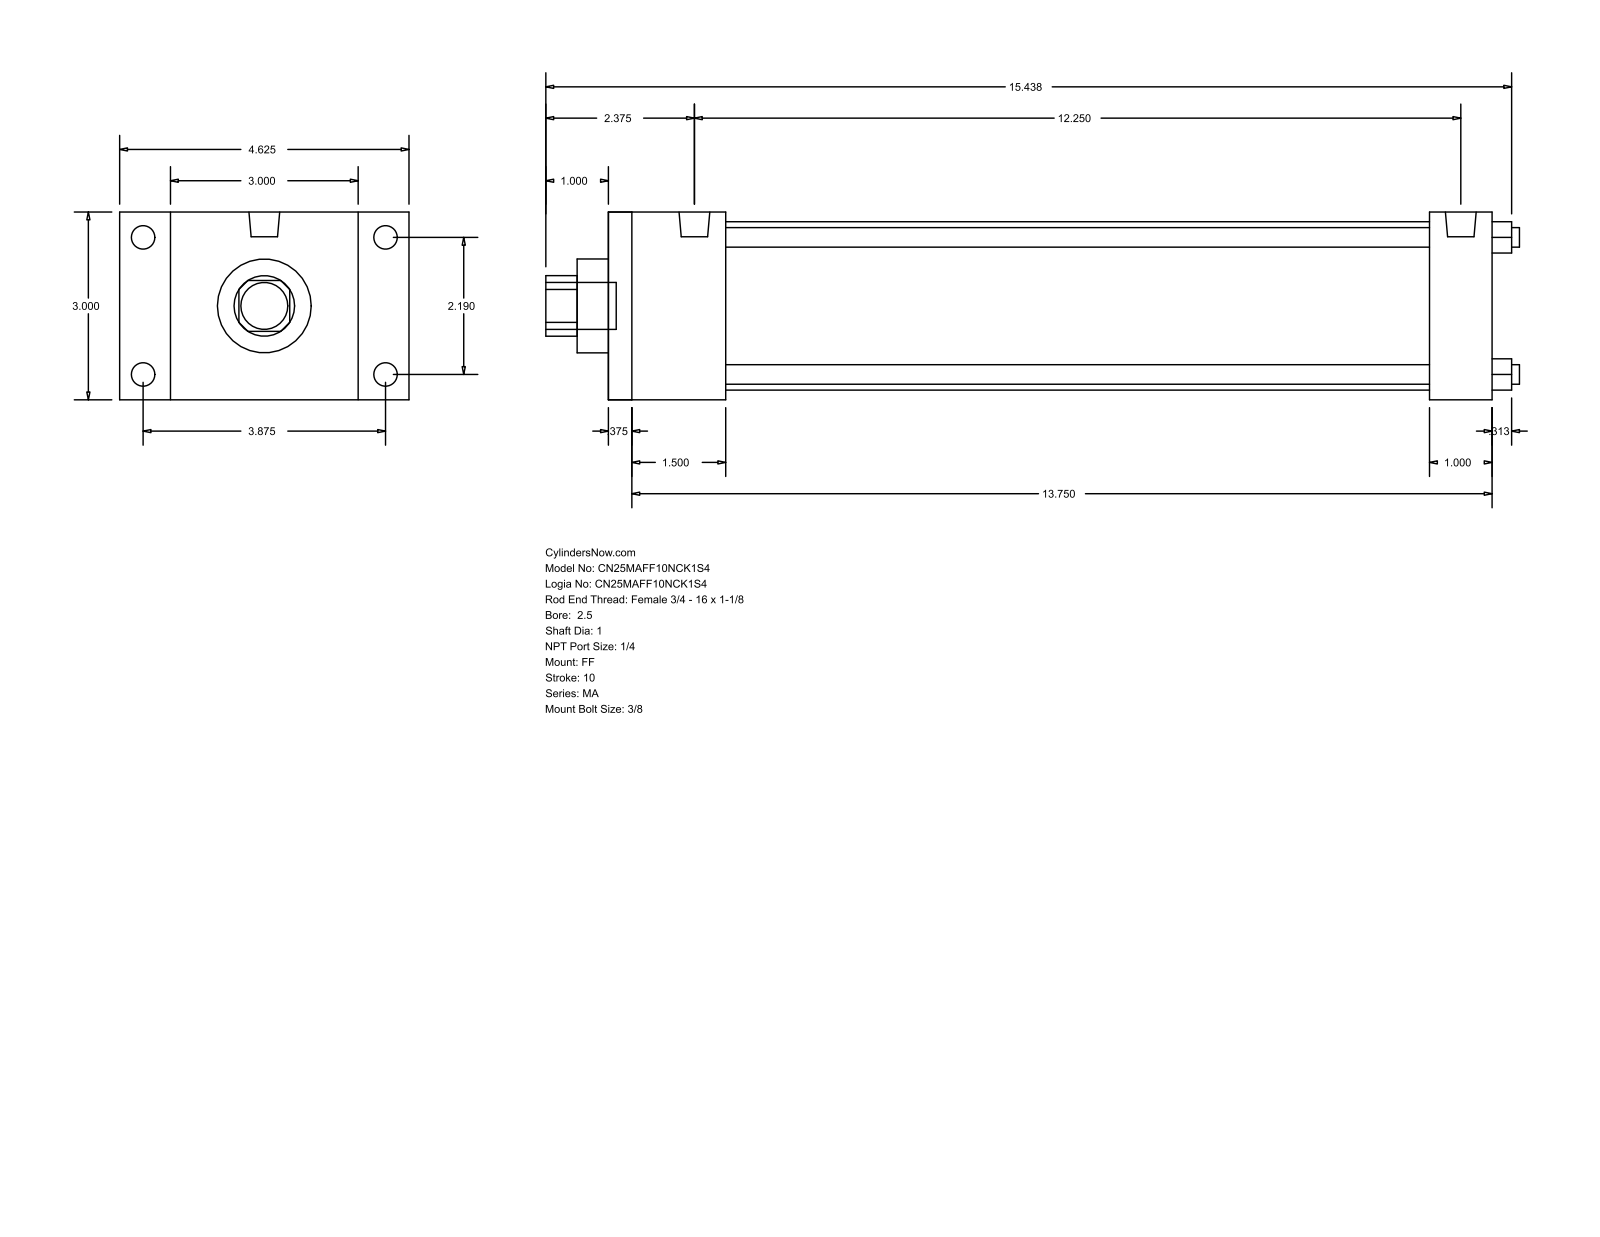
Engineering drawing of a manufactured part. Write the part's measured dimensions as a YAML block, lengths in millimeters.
part_name: "MA_FF__0250_1"
step_written_by: "GSSL Pune (CONFIG_CONTROL_DESIGN)"
units: millimeters
bodies: {solids: 0, faces: 92, planar: 64, cylindrical: 28, other: 0}
overall_size: [395.29, 117.47, 76.2]
round_holes:
  - {diameter: 7.94, count: 4}
  - {diameter: 25.4, count: 1}
  - {diameter: 38.1, count: 1}
  - {diameter: 68.33, count: 1}
round_bosses_or_shafts:
  - {diameter: 9.53, count: 4}
  - {diameter: 7.94, count: 4}
  - {diameter: 12.49, count: 2}
  - {diameter: 19.05, count: 1}
partial_cylinders:
  - {radius: 12.29, count: 1}
face_to_face_distances: [76.2, 358.78, 9.52, 349.26, 47.63, 333.37, 38.11, 323.85, 285.74, 311.15]
hole_center_spacings: [39.33, 55.62, 78.66]
